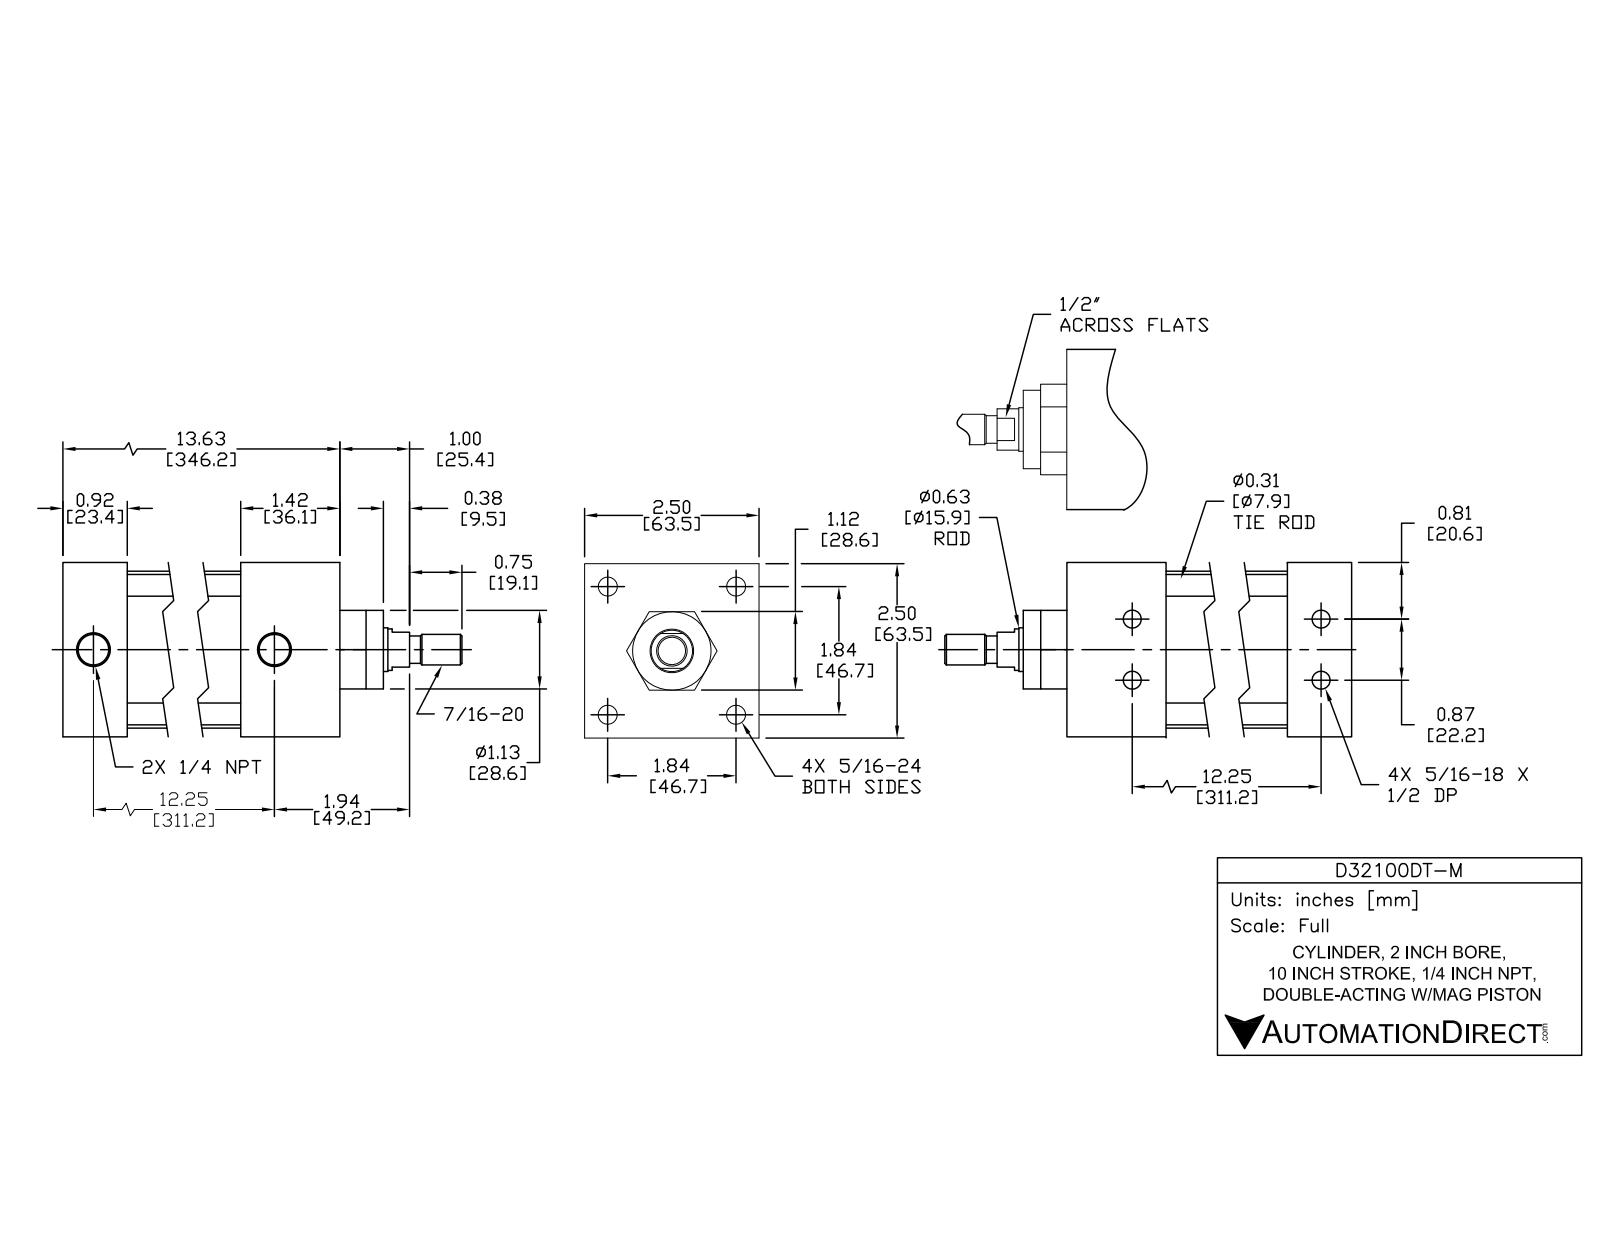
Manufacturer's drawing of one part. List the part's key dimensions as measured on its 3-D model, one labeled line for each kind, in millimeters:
Part name (STEP PRODUCT): D32100DT-M; D32100DT-M PISTON; D32100DT-M BODY
STEP written by: SolidWorks 2015 (AUTOMOTIVE_DESIGN)
Units: millimetres
Bodies: 12 solids, 298 faces (94 planar, 114 cylindrical, 90 other)
Overall size (bounding box): 390.4 × 63.5 × 63.5
Volume: 552 600 mm³ · Surface area: 201 300 mm²
Round holes (diameter × count): ⌀6.4 ×4, ⌀6.8 ×4, ⌀9.1 ×4, ⌀12.7 ×4, ⌀7.5 ×2, ⌀12.1 ×2, ⌀15.9 ×1, ⌀16 ×1, ⌀50.8 ×1
Round bosses / shafts (diameter × count): ⌀12.3 ×4, ⌀8 ×4, ⌀7.2 ×4, ⌀57.2 ×1, ⌀50.7 ×1, ⌀28.4 ×1, ⌀15.8 ×1, ⌀15 ×1
Partial cylindrical surfaces — rounded edges, fillets, slot ends (radius × count): R6.4 ×4
Main face-to-face distances: 63.5, 2, 284.5, 346, 36.1, 309.9, 322.6, 286.5, 23.4, 25.4
Hole centre spacings: 33.2, 46.9, 311.2, 311, 11.1, 11.1, 22.2, 66.4
